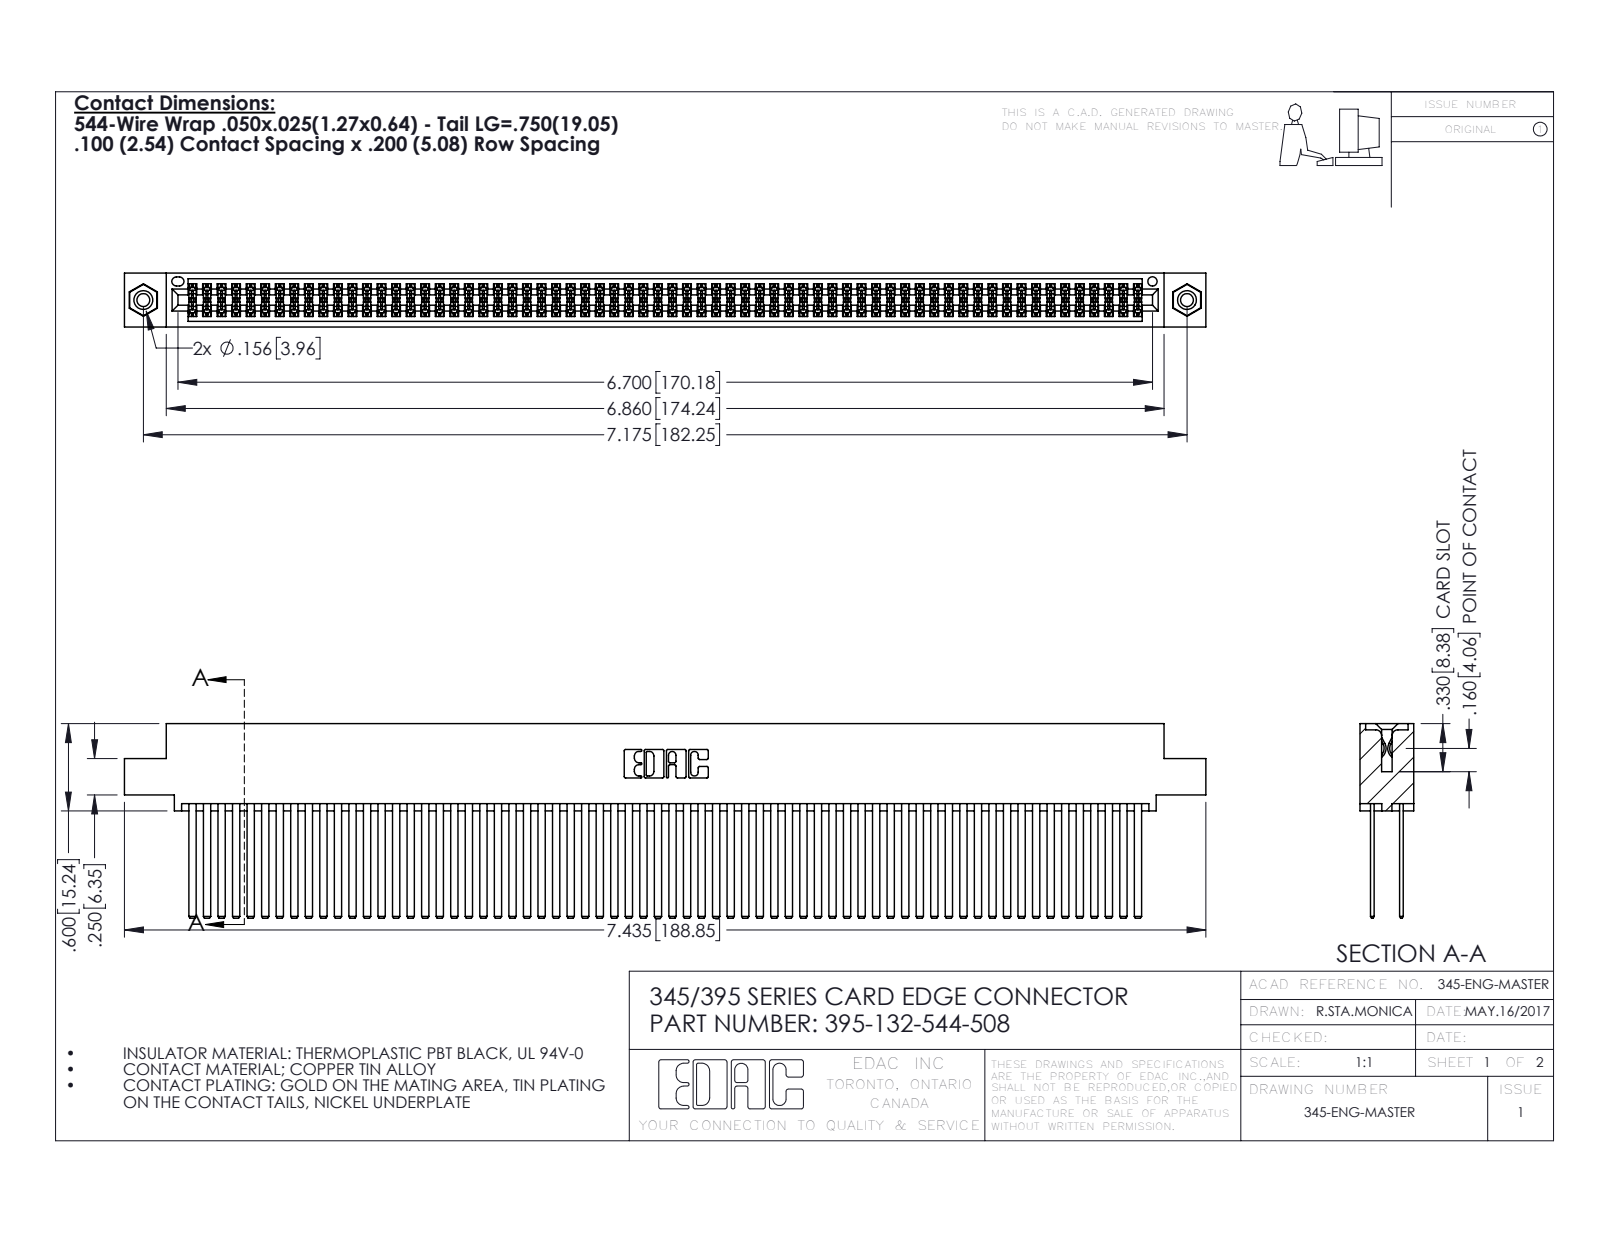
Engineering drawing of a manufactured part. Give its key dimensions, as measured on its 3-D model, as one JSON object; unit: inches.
{"part_name": "345-292-001_345-293-144; 395-132-544-508; 345 Part_0.110 Offset - 0.156 Dia-TI; 345-250-001_345-250-003-102", "step_written_by": "SolidWorks 2016 (CONFIG_CONTROL_DESIGN)", "units": "inches", "bodies": {"solids": 135, "faces": 5998, "planar": 3944, "cylindrical": 2038, "other": 16}, "overall_size": [7.435, 1.337, 0.37], "volume_in3": 1.241, "surface_area_in2": 55.89, "round_holes": [[0.089, 2], [0.125, 2], [0.156, 2], [0.064, 1]], "round_bosses_or_shafts": [[0.155, 2]], "partial_cylinders_radius": [[0.006, 198], [0.01, 22], [0.007, 6], [0.031, 6], [0.026, 3], [0.014, 2], [0.019, 2], [0.022, 2]], "face_to_face_distances": [0.2, 0.025, 0.072, 0.098, 0.272, 0.298, 0.225, 0.175, 0.37, 0.149], "hole_center_spacings": [0.27, 6.939, 7.175]}
